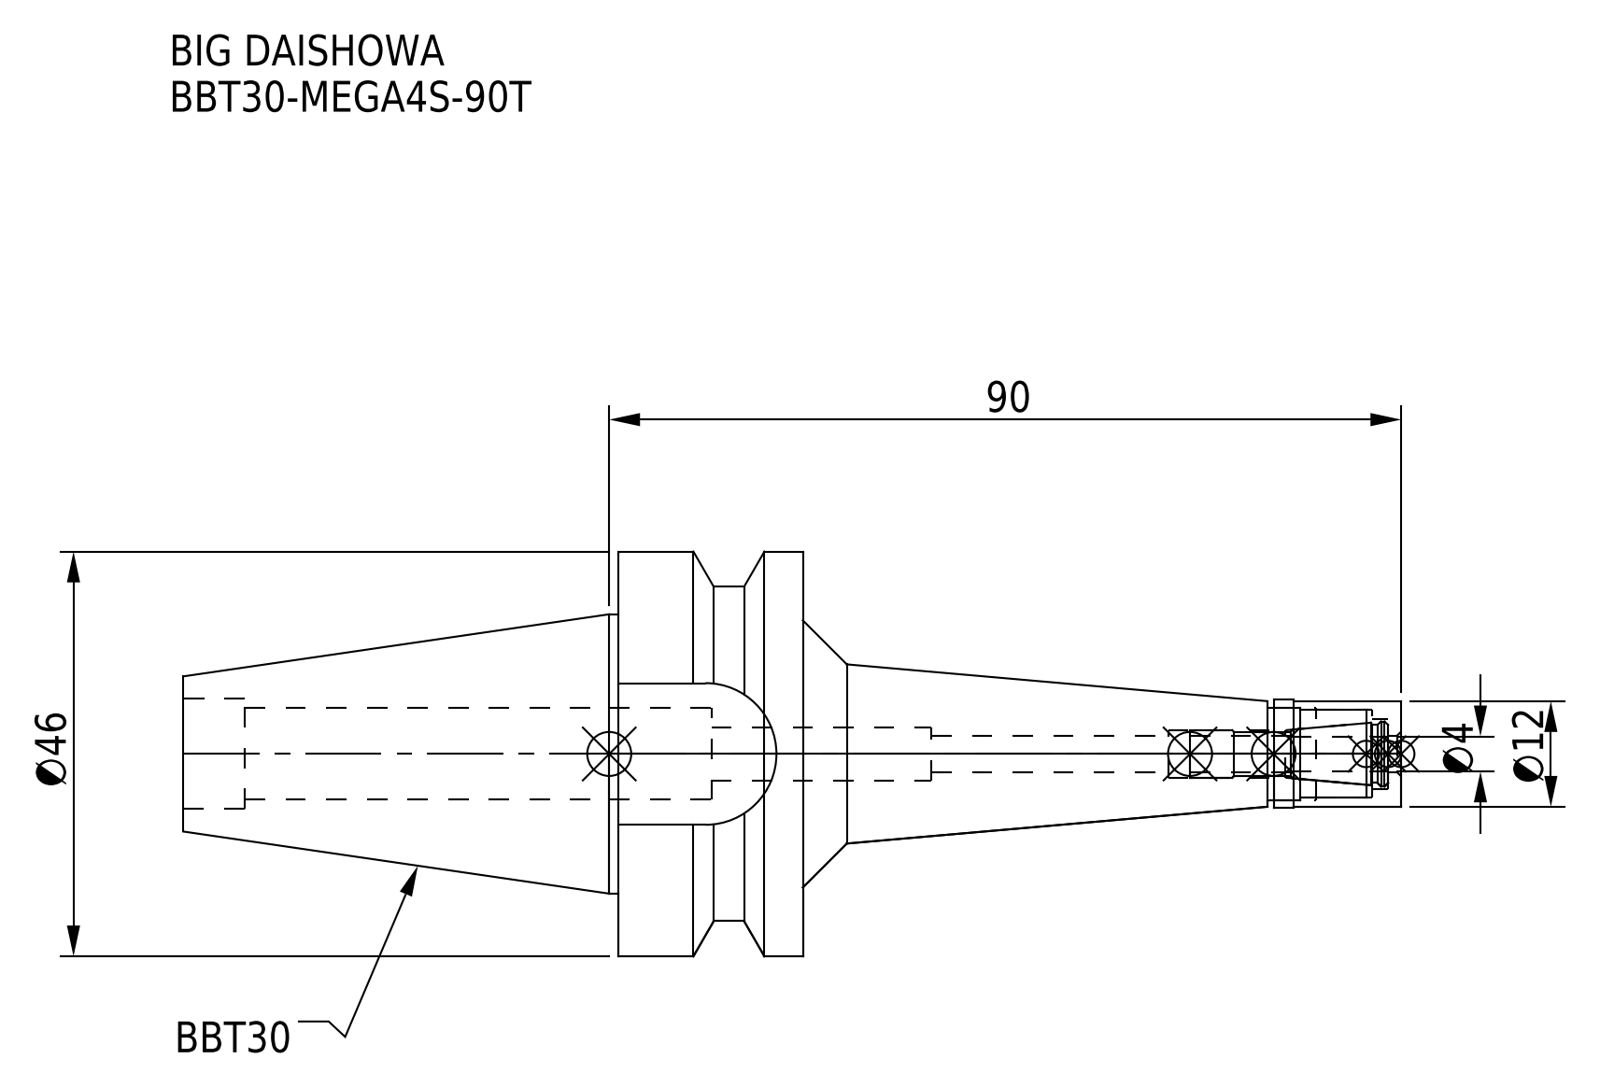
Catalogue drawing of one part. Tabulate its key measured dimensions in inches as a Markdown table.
| quantity | value |
| --- | --- |
| part name | BBT30MS04090T-040_ASM.stp; DXF_TEMP_ASSY_ASM_4_ASM.stp; BBT30-MEGA4S-90T-FreeParts; BBT30-MEGA4S-90T (+3 more) |
| STEP written by | SolidWorks 2019 (CONFIG_CONTROL_DESIGN) |
| units | inches |
| bodies | 2 solids, 74 faces (22 planar, 38 cylindrical, 14 other) |
| overall size | 5.449 × 1.811 × 1.811 |
| volume | 3.719 in³ |
| surface area | 26.9 in² |
| round holes (diameter × count) | 0.161 × 1, 0.165 × 1, 0.213 × 1, 0.236 × 1, 0.315 × 1, 0.394 × 1, 0.409 × 1, 0.413 × 1, 0.492 × 1 |
| round bosses / shafts (diameter × count) | 1.811 × 1, 1.25 × 1, 0.484 × 1, 0.472 × 1 |
| partial cylindrical surfaces (radius × count) | 0.317 × 1, 0.748 × 1 |
| main face-to-face distances | 0.827, 1.283, 1.945, 2.772, 0.634, 2.677, 3.504, 5.449, 0.028, 3.087 |
